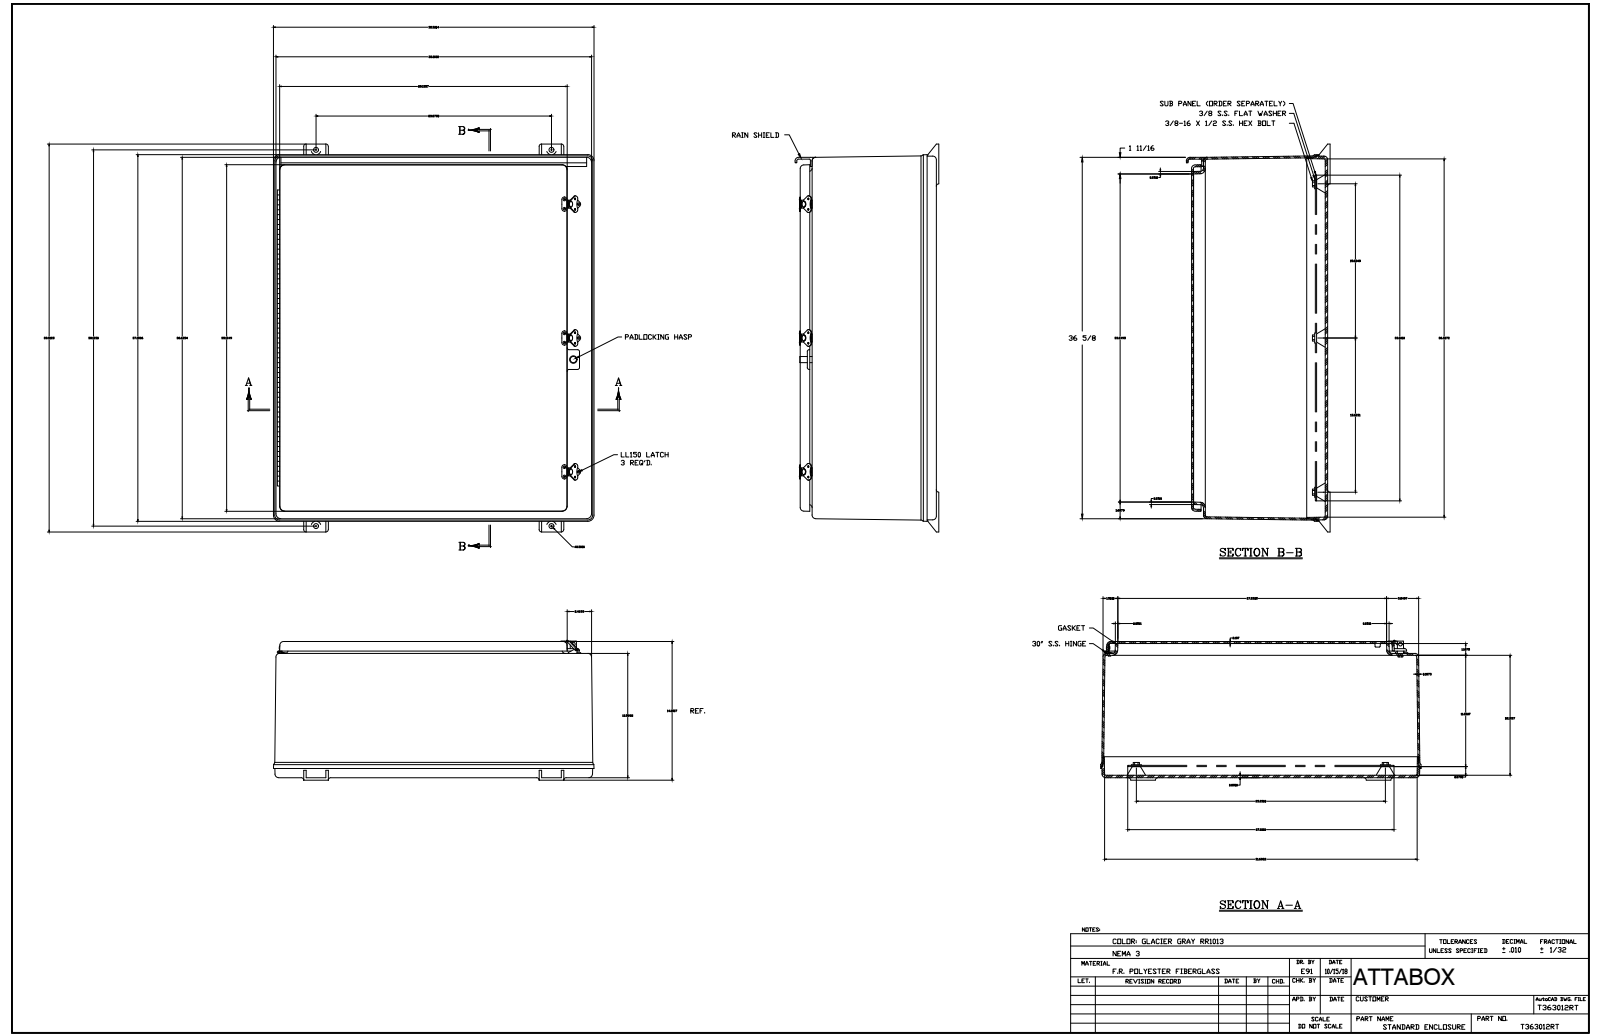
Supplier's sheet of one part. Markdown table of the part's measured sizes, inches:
| quantity | value |
| --- | --- |
| part name | T363012RT |
| STEP written by | SolidWorks 2018 (AUTOMOTIVE_DESIGN) |
| units | inches |
| bodies | 49 solids, 1486 faces (573 planar, 602 cylindrical, 311 other) |
| overall size | 39.313 × 32.5 × 14.594 |
| volume | 943.1 in³ |
| surface area | 9 527 in² |
| round holes (diameter × count) | 0.13 × 27, 0.063 × 12, 0.065 × 7, 0.138 × 6, 0.187 × 6, 0.065 × 4, 0.563 × 4, 0.433 × 2, 0.51 × 2, 0.51 × 2, 0.125 × 1, 0.135 × 1 |
| round bosses / shafts (diameter × count) | 0.14 × 12, 0.297 × 11, 0.5 × 3, 0.25 × 1, 0.201 × 1, 0.2 × 1, 0.135 × 1 |
| partial cylindrical surfaces (radius × count) | 0.01 × 86, 0.25 × 24, 0.188 × 17, 0.312 × 17, 0.375 × 13, 0.03 × 12, 0.5 × 12, 0.016 × 8 |
| main face-to-face distances | 0.25, 0.188, 13.563, 13.813, 13.624, 13.374, 0.187, 0.188, 12.594, 1.219 |
| hole center spacings | 13.563, 9.5, 19.5, 27.125, 3.474, 13.583, 15.625, 19.044 |
